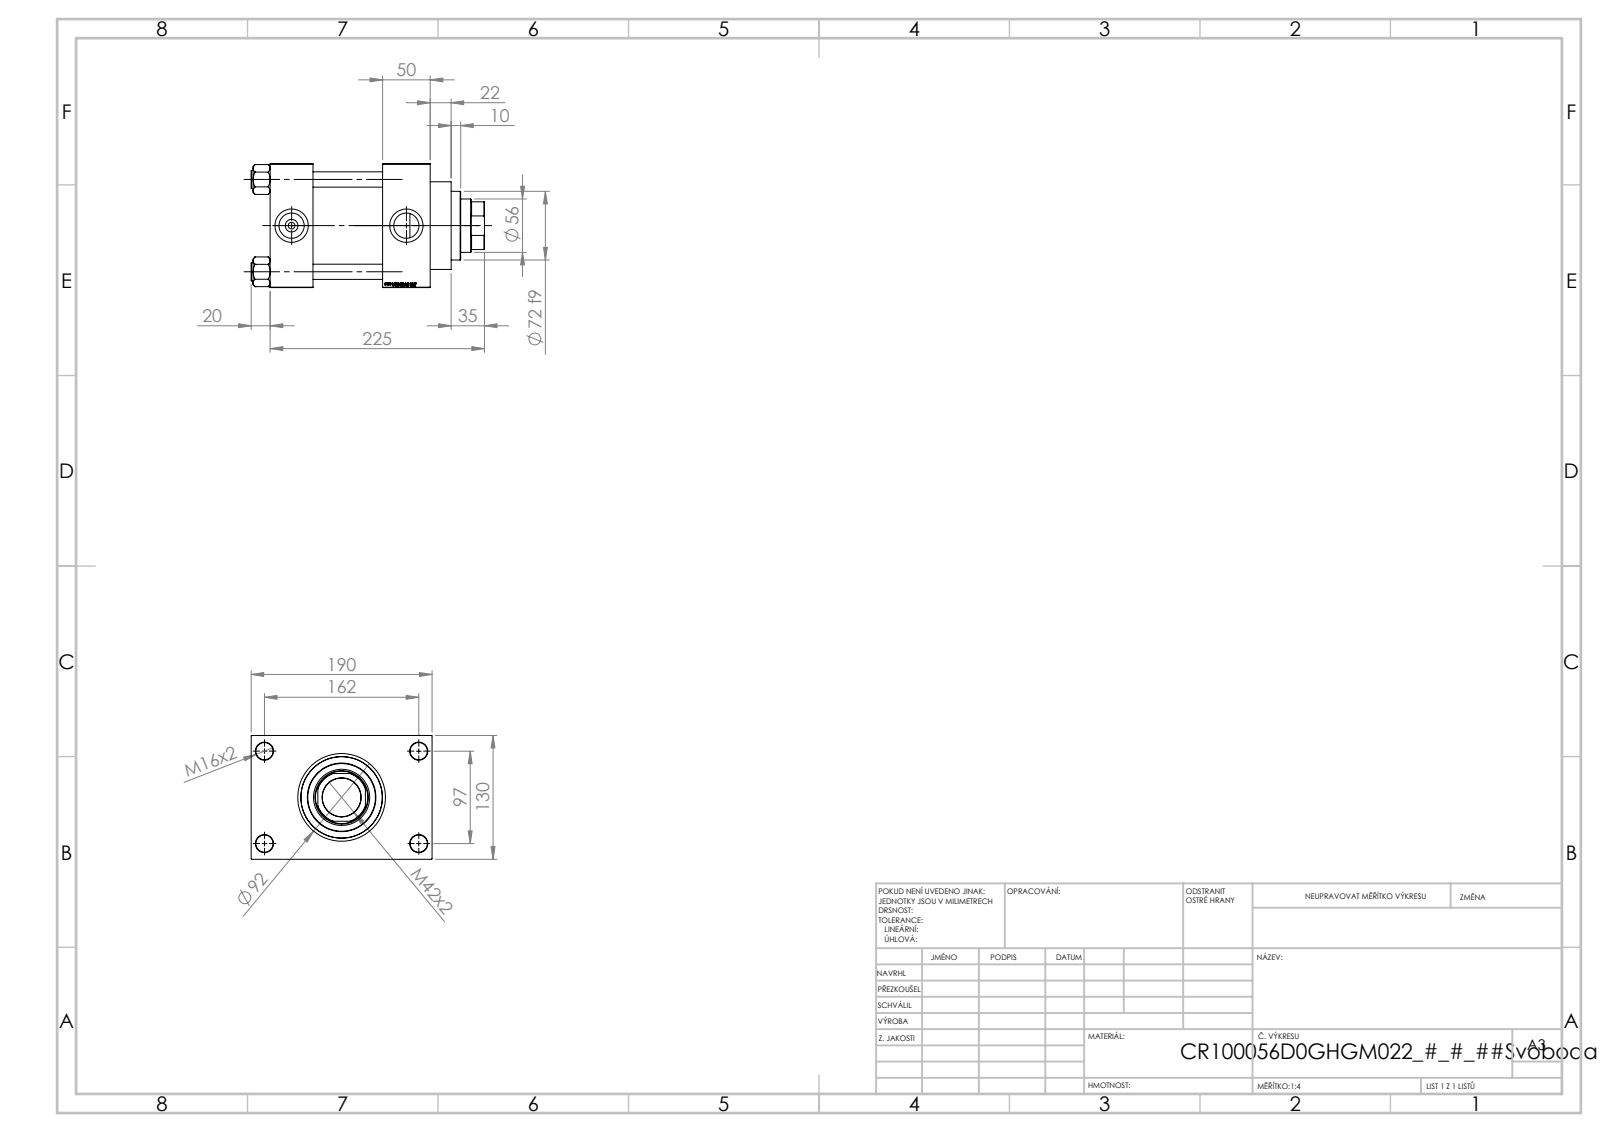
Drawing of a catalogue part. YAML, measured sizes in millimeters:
part_name: "V215CR_VCP_D; NUT_M5_D; V215CR_D_Body; V215_VC_A (+1 more)"
step_written_by: "SolidWorks 2019 (CONFIG_CONTROL_DESIGN)"
units: millimeters
bodies: {solids: 11, faces: 1151, planar: 545, cylindrical: 88, other: 518}
overall_size: [245, 190, 130]
volume: 2637000
surface_area: 364411
round_holes:
  - {diameter: 16, count: 4}
  - {diameter: 18, count: 4}
  - {diameter: 7, count: 2}
  - {diameter: 26.44, count: 2}
  - {diameter: 35, count: 2}
  - {diameter: 40.5, count: 1}
  - {diameter: 56, count: 1}
  - {diameter: 59, count: 1}
  - {diameter: 76, count: 1}
  - {diameter: 85.5, count: 1}
  - {diameter: 100, count: 1}
round_bosses_or_shafts:
  - {diameter: 19, count: 4}
  - {diameter: 106, count: 1}
  - {diameter: 92, count: 1}
  - {diameter: 72, count: 1}
partial_cylinders:
  - {radius: 27, count: 1}
face_to_face_distances: [130, 50, 45, 118, 73, 123, 168, 30, 160, 190]
hole_center_spacings: [32.55, 68.52, 94.41, 96.9, 102.27, 129.45, 161.73, 97]
